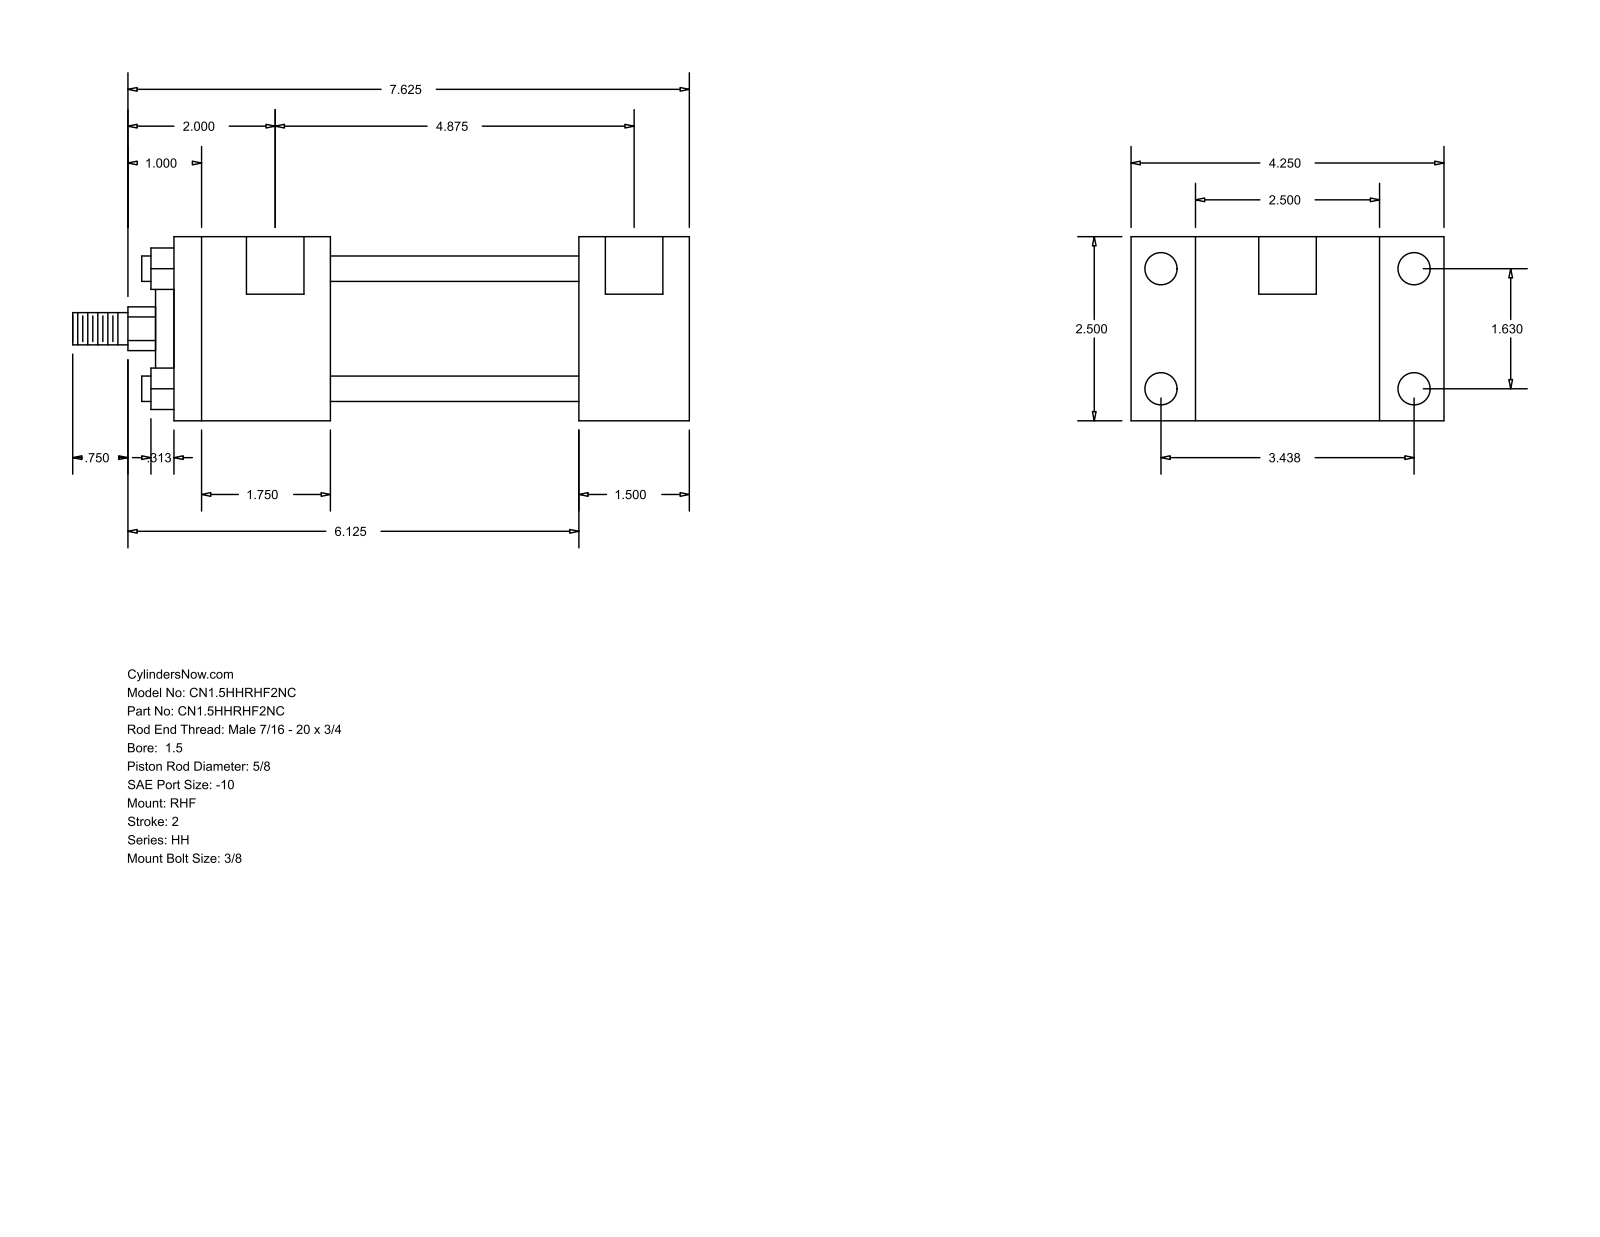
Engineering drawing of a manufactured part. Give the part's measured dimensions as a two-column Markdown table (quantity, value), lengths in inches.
| quantity | value |
| --- | --- |
| part name | HH_RHF__0150_0.625 |
| STEP written by | GSSL Pune (CONFIG_CONTROL_DESIGN) |
| units | inches |
| bodies | 0 solids, 88 faces (60 planar, 28 cylindrical, 0 other) |
| overall size | 8.375 × 4.25 × 2.5 |
| round holes (diameter × count) | 0.219 × 4, 0.438 × 4, 0.781 × 2 |
| round bosses / shafts (diameter × count) | 0.345 × 4, 1.75 × 1, 1.125 × 1, 0.625 × 1, 0.437 × 1 |
| partial cylindrical surfaces (radius × count) | 0.297 × 1 |
| main face-to-face distances | 2.5, 0.875, 3.375, 1.5, 5.5, 7, 4.25, 3.375, 2.125, 4.875 |
| hole center spacings | 0.063, 1.63, 3.438, 3.805, 4.937, 5, 4.875 |
